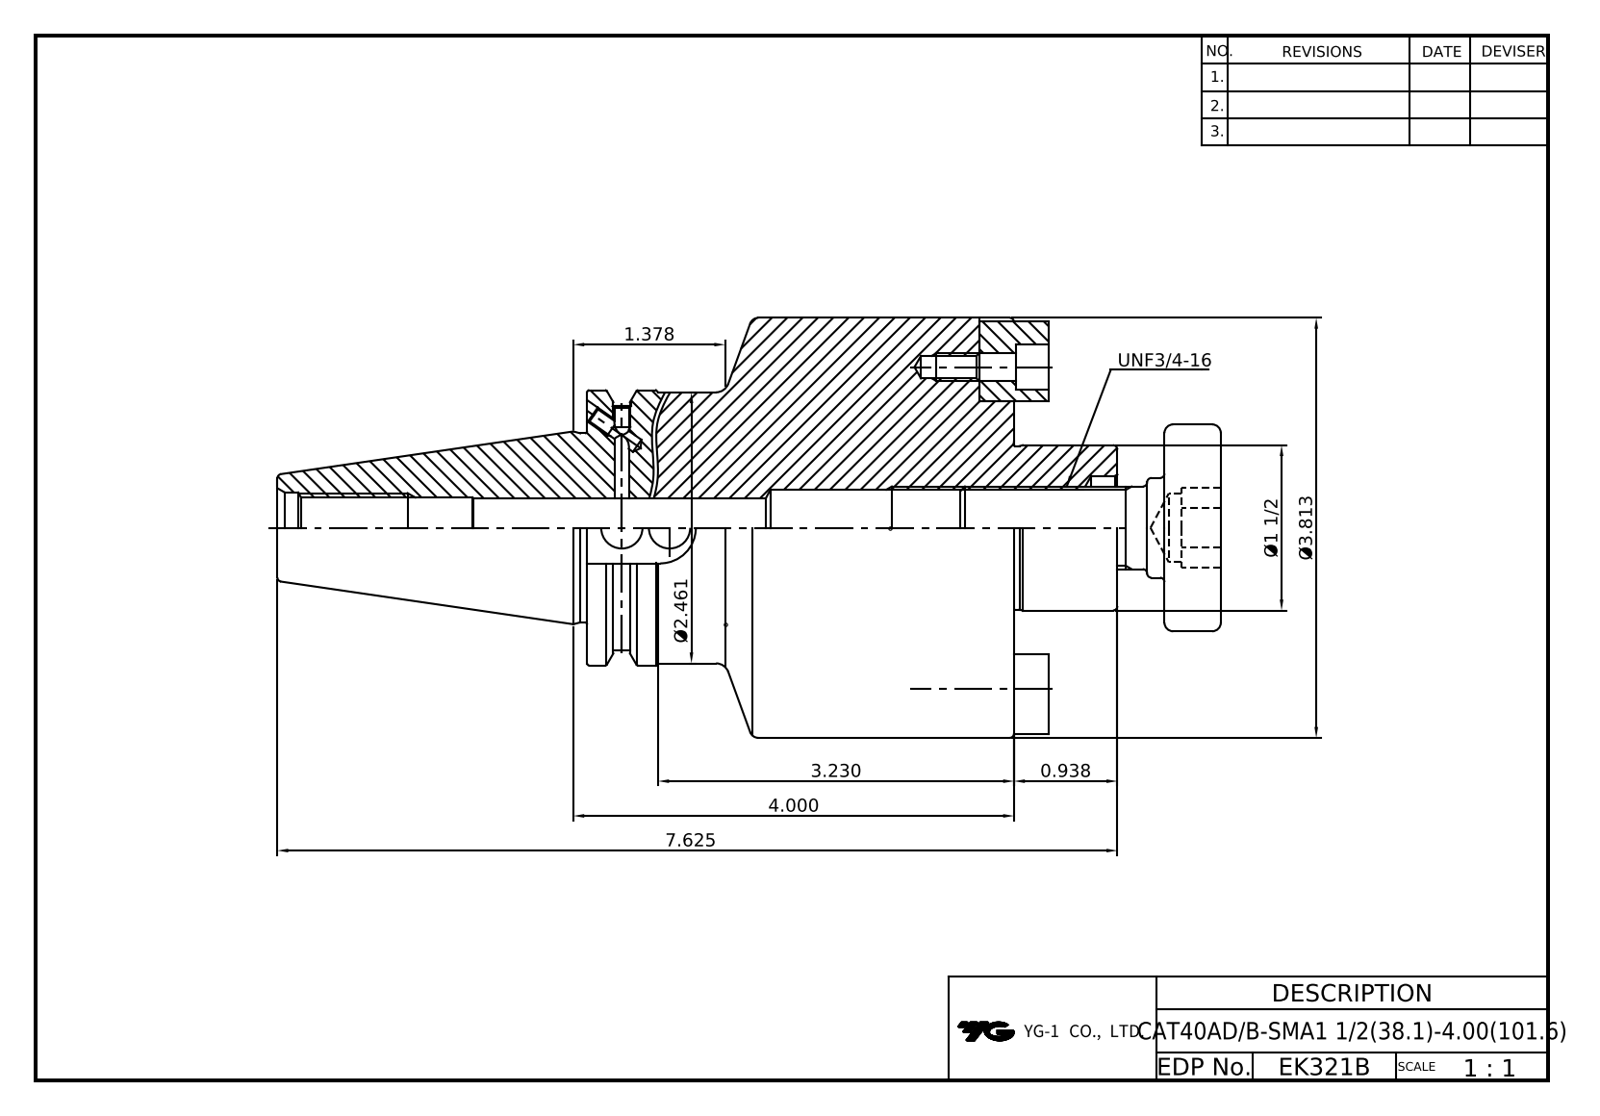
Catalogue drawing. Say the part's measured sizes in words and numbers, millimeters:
The part is named "LO-CAT40ADB-SMA38.1-101.6; HEX'' WRENCH BOLT-UNC1_4-20x5_8L; DRIVE KEY-15.875x15.875x18.5; COLLAR BOLT-UNF3_4-16x47L". Its 3-D file was written by "Autodesk Inventor 2022 (AUTOMOTIVE_DESIGN)". It is 6 solids with 176 faces: 83 planar, 50 cylindrical and 43 other. Overall it measures 201.3 by 96.9 by 96.9 millimeters. Its volume is 665 000 cubic millimeters and its surface area 74 710 square millimeters. Round holes: 4 of diameter 3.3, 2 of diameter 4, 2 of diameter 4.2, 2 of diameter 5, 2 of diameter 6.6, 2 of diameter 10.3, 1 of diameter 9.5, 1 of diameter 13, 1 of diameter 13.4, 1 of diameter 15.9, 1 of diameter 16.3, 1 of diameter 17.3. Round bosses or shafts: 2 of diameter 9.5, 2 of diameter 6.4, 1 of diameter 96.9, 1 of diameter 63.5, 1 of diameter 62.5, 1 of diameter 47.7, 1 of diameter 43.6, 1 of diameter 38.1. Partial cylindrical surfaces (rounded edges, fillets, slot ends): 2 of radius 7.9, 1 of radius 8.2, 1 of radius 28.1. The main face-to-face distances are 31.4, 98.4, 129.9, 116.9, 18.4, 13, 90.5, 8, 26.4, 39.4. The hole center spacings are 37.1, 74.1.
